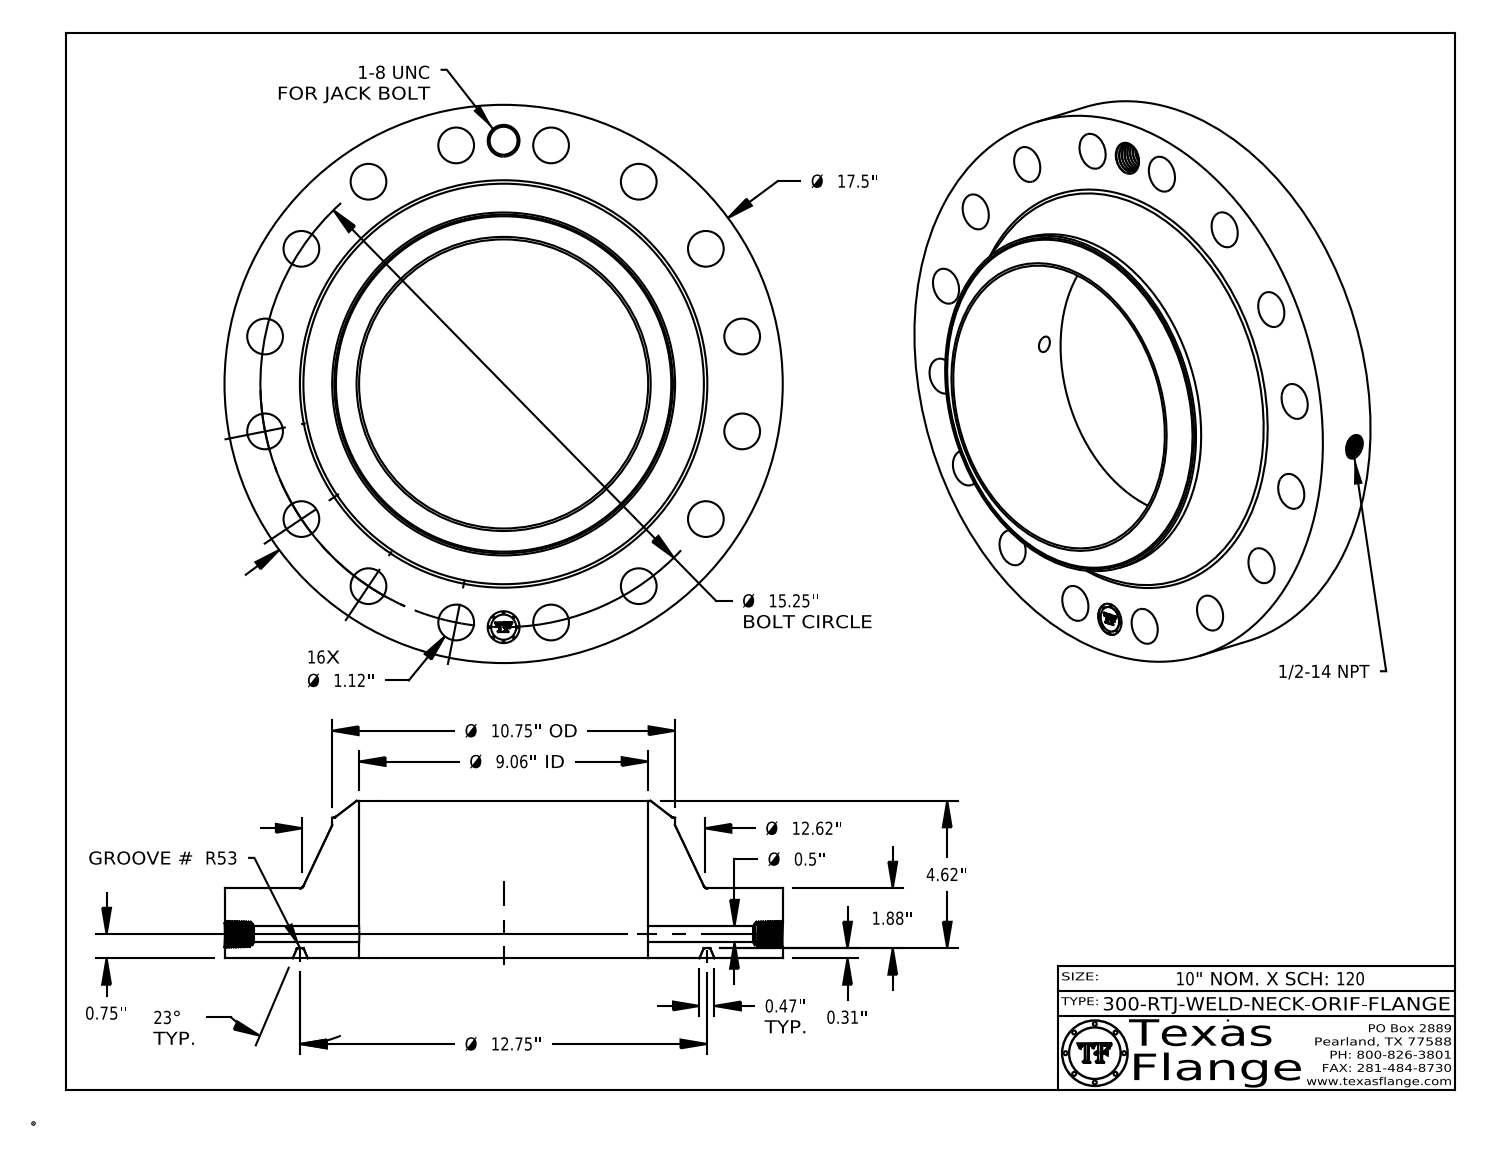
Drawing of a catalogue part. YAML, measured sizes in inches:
part_name: "300-RTJ-WELD-NECK"
step_written_by: "CATIA V5 STEP AP214 (AUTOMOTIVE_DESIGN)"
units: inches
bodies: {solids: 1, faces: 813, planar: 370, cylindrical: 112, other: 331}
overall_size: [17.5, 17.5, 4.933]
volume: 441.5
surface_area: 804.3
round_holes:
  - {diameter: 1.12, count: 16}
  - {diameter: 0.5, count: 1}
  - {diameter: 0.672, count: 1}
  - {diameter: 0.875, count: 1}
  - {diameter: 1, count: 1}
  - {diameter: 9.062, count: 1}
round_bosses_or_shafts:
  - {diameter: 0.061, count: 8}
  - {diameter: 17.5, count: 1}
  - {diameter: 10.75, count: 1}
  - {diameter: 0.788, count: 1}
face_to_face_distances: [2.193, 0.313, 1.88, 4.933, 4.62, 2.74, 0.015, 2.178, 1.865, 2.755]
hole_center_spacings: [5.836, 7.625, 10.783, 14.089, 14.957, 2.975, 2.975, 8.472]
